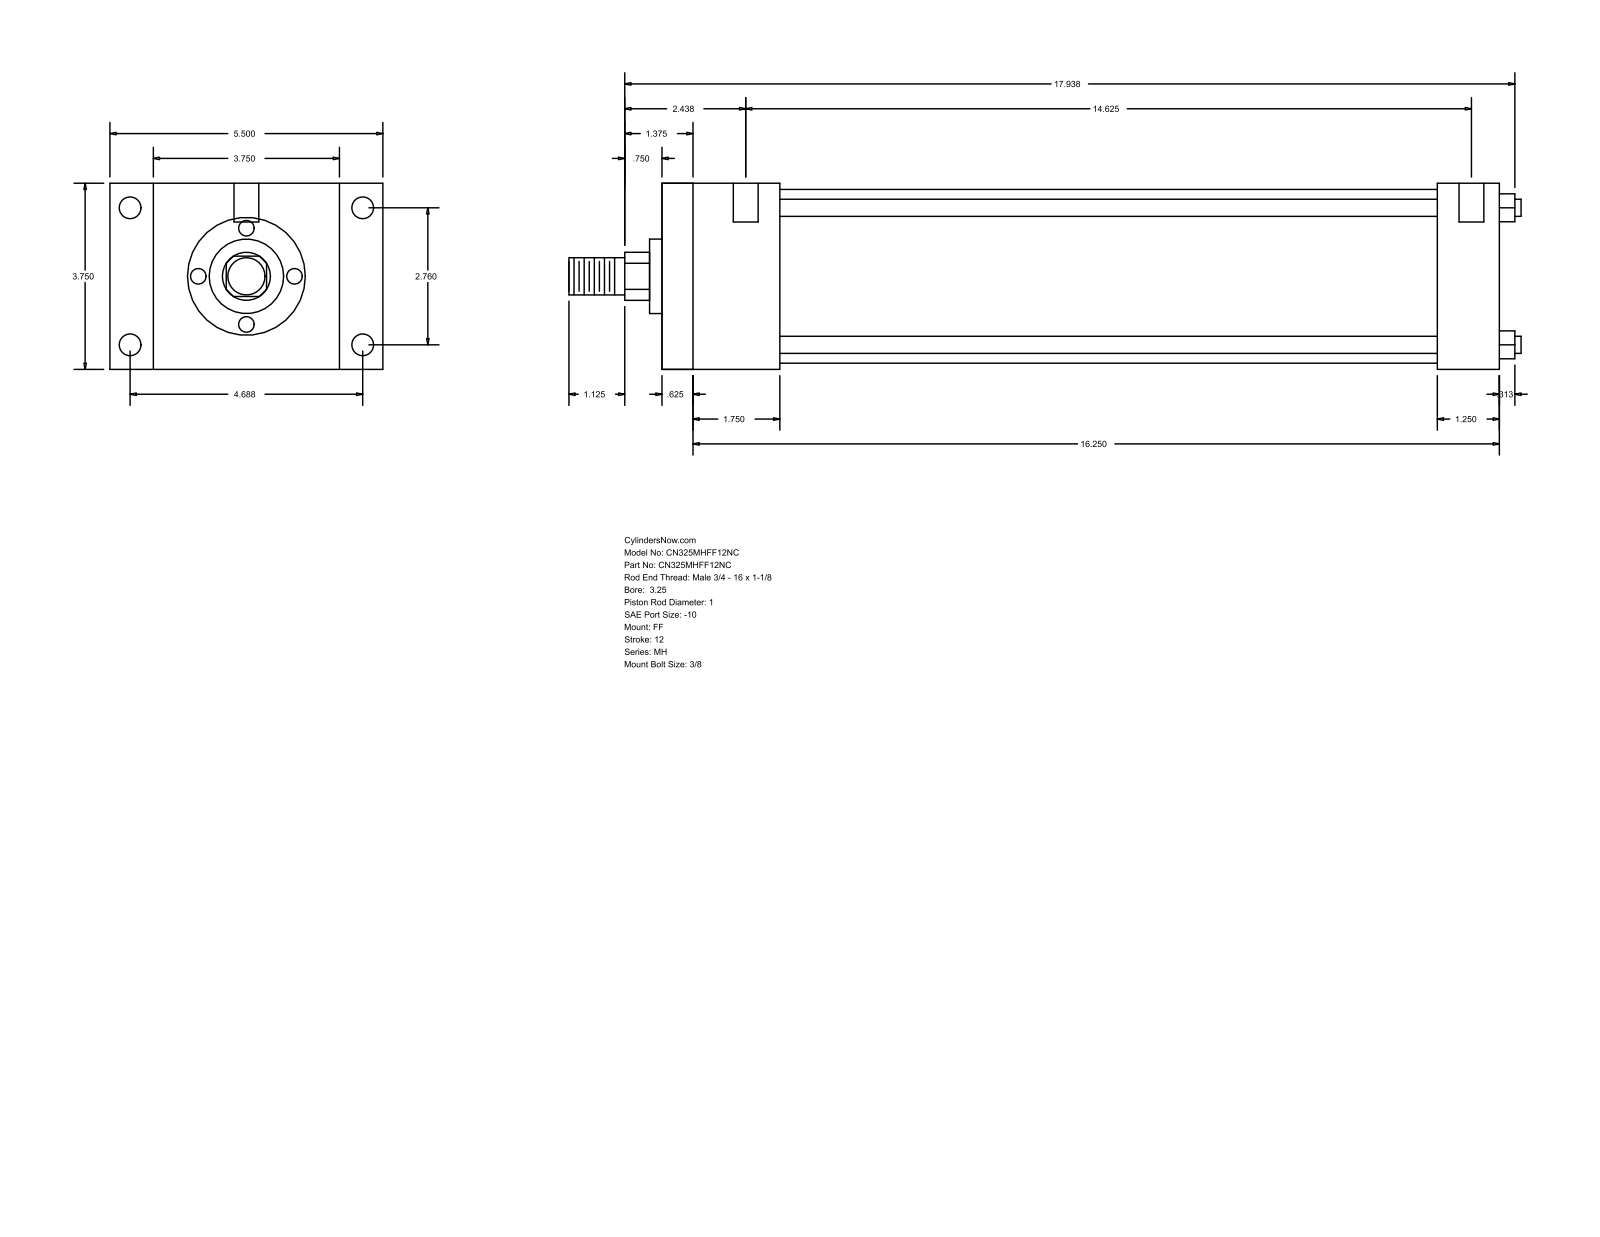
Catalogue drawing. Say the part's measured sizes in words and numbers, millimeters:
The part is named "MH_FF__0325_1". Its 3-D file was written by "GSSL Pune (CONFIG_CONTROL_DESIGN)". It is 0 solids with 92 faces: 64 planar, 28 cylindrical and 0 other. Overall it measures 487.36 by 139.7 by 95.25 millimeters. Round holes: 4 of diameter 5.56, 4 of diameter 11.13, 2 of diameter 12.7. Round bosses or shafts: 4 of diameter 8.76, 1 of diameter 88.9, 1 of diameter 38.1, 1 of diameter 25.4, 1 of diameter 19.05. Partial cylindrical surfaces (rounded edges, fillets, slot ends): 1 of radius 12.29. The main face-to-face distances are 95.24, 428.63, 15.87, 412.76, 22.23, 117.47, 396.88, 381.01, 31.75, 60.33. The hole center spacings are 70.1, 119.06, 138.16, 377.82, 1.58, 4.76, 371.48, 373.06.
